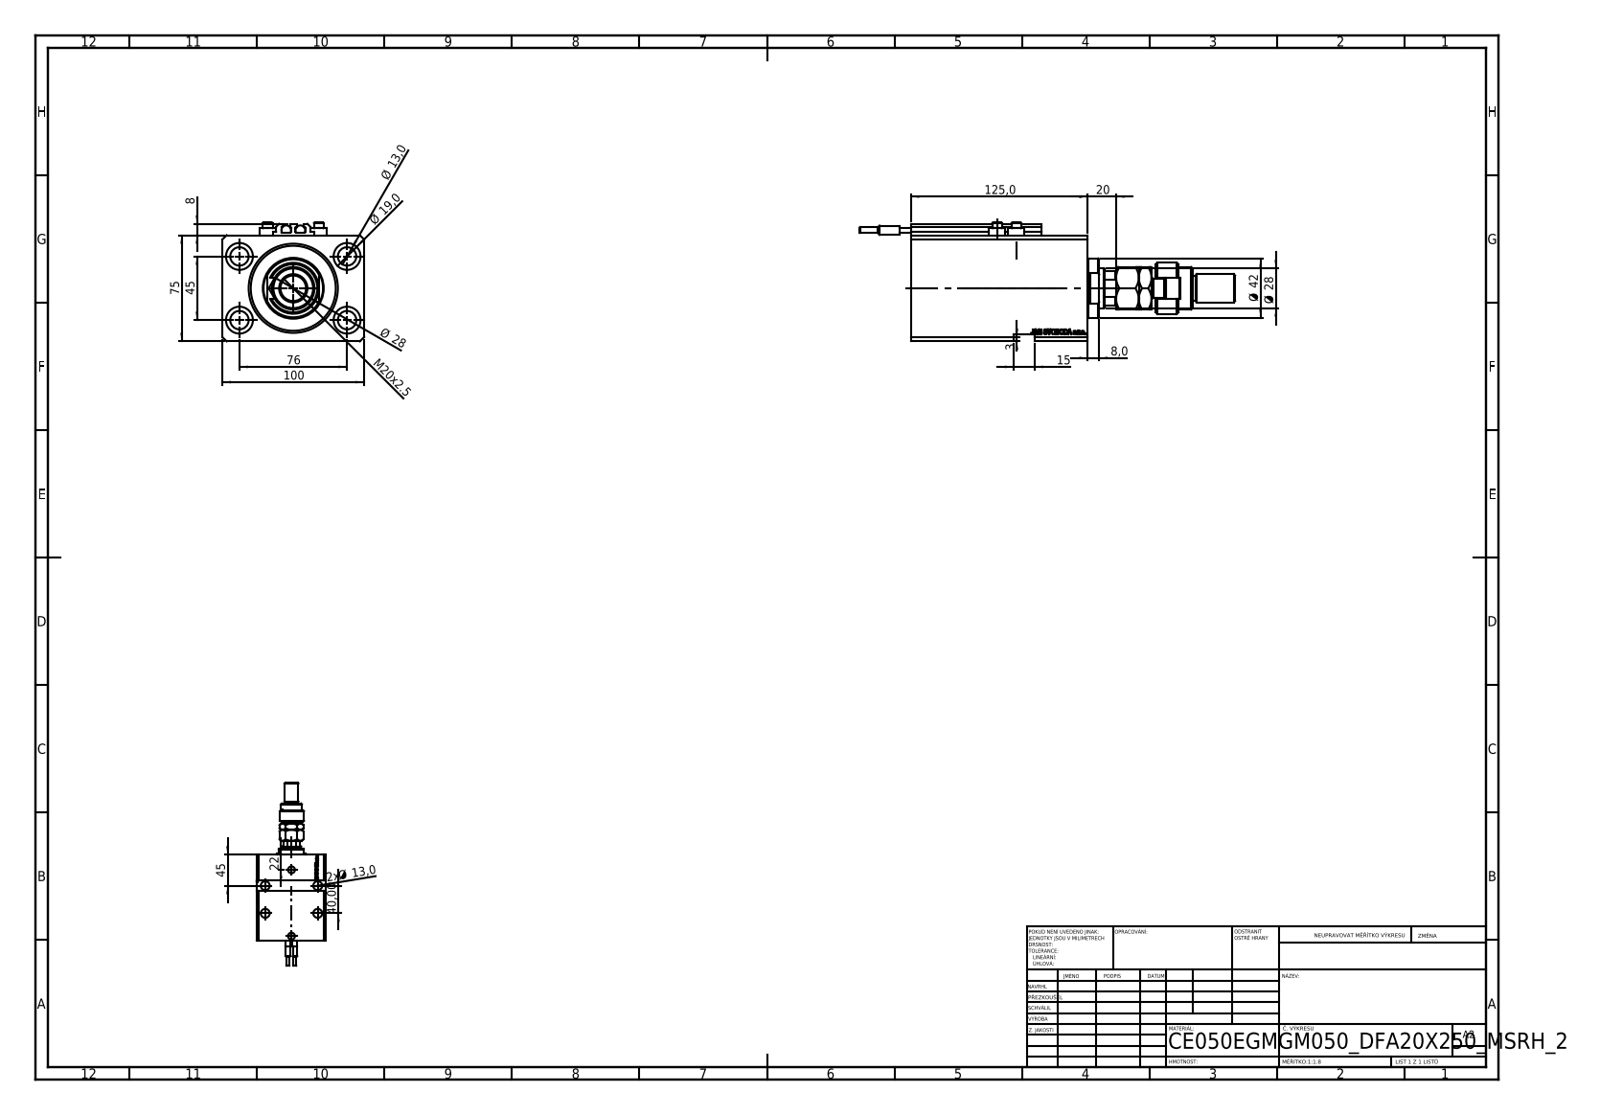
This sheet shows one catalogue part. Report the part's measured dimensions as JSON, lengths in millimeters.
{"part_name": "V250CE_E_Body; V250CE_VC_E; ALLEN BOLT V250CE; V250CE_C_VCP (+3 more)", "step_written_by": "SolidWorks 2019 (CONFIG_CONTROL_DESIGN)", "units": "millimeters", "bodies": {"solids": 12, "faces": 1245, "planar": 595, "cylindrical": 171, "other": 479}, "overall_size": [265, 100, 84], "volume_mm3": 821304, "surface_area_mm2": 166342, "round_holes": [[13, 8], [1.25, 4], [4, 4], [19, 4], [10, 2], [13.16, 2], [20, 2], [18.5, 1], [28, 1], [50, 1], [63, 1]], "round_bosses_or_shafts": [[11.6, 4], [7, 4], [6.8, 2], [6.5, 2], [4, 2], [42, 1], [36, 1], [30, 1]], "partial_cylinders_radius": [[0.2, 10], [7.5, 1], [12, 1], [13.5, 1]], "face_to_face_distances": [75, 100, 20, 125, 11.9, 113.1, 105, 93.1, 70, 3], "hole_center_spacings": [44.16, 76, 13.6, 20.72, 27.59, 29, 33.62, 36]}
